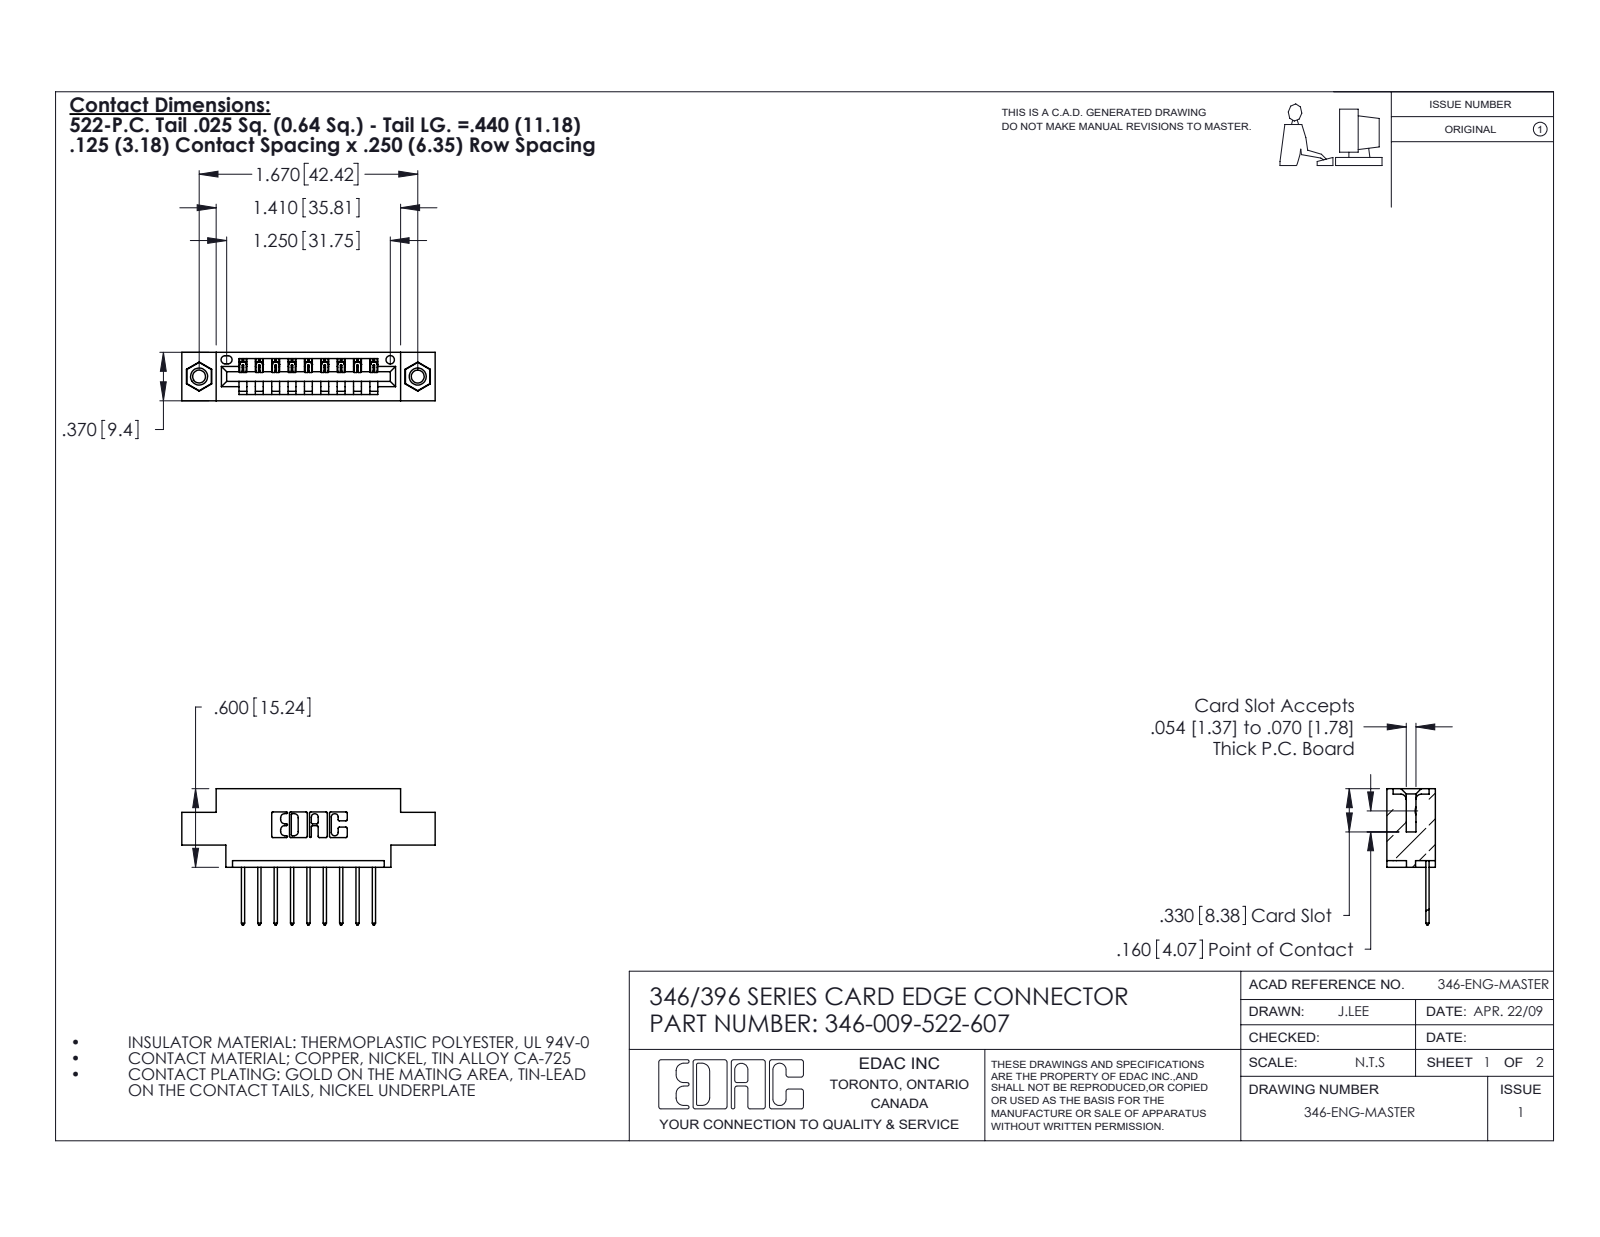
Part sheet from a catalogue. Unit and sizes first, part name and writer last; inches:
Units: inches
Overall size (bounding box): 1.935 × 1.04 × 0.37
Round holes (diameter × count): ⌀0.098 ×2, ⌀0.125 ×2, ⌀0.156 ×2, ⌀0.064 ×1
Round bosses / shafts (diameter × count): ⌀0.155 ×2
Partial cylindrical surfaces — rounded edges, fillets, slot ends (radius × count): R0.01 ×22, R0.006 ×18, R0.01 ×18, R0.007 ×6, R0.031 ×6, R0.026 ×3, R0.031 ×2, R0.04 ×2
Main face-to-face distances: 0.25, 0.37, 0.048, 0.322, 0.222, 0.072, 0.298, 0.025, 0.148, 0.1
Hole centre spacings: 0.246, 1.465, 1.67
Volume: 0.263 in³ · Surface area: 8.152 in²
Bodies: 12 solids, 708 faces (472 planar, 220 cylindrical, 16 other)
Part name (STEP PRODUCT): 346 Part_0.170 Offset - 0.156 Dia-TI; 346-009-522-607; 345-292-001_345-293-122; 345-250-001_345-250-005-103
STEP written by: SolidWorks 2020 (CONFIG_CONTROL_DESIGN)
